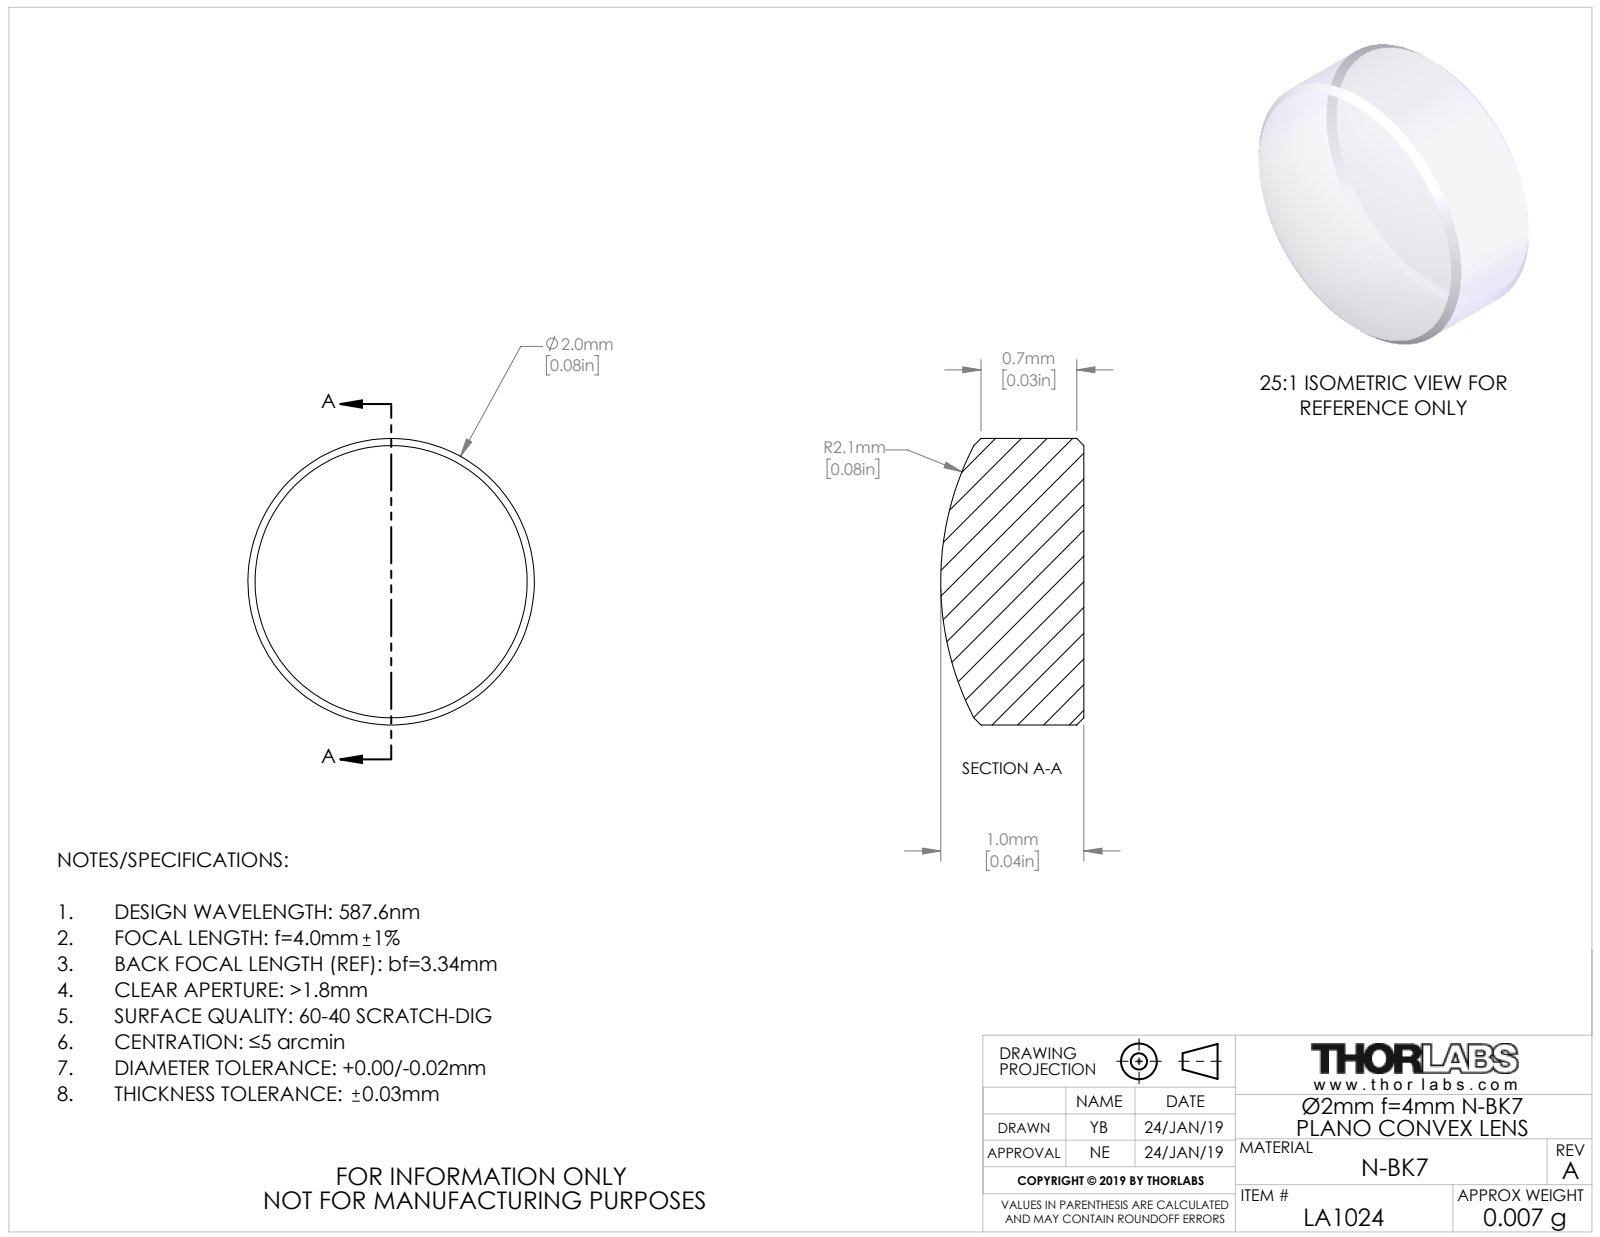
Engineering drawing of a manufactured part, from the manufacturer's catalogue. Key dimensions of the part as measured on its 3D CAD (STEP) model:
Part name (STEP PRODUCT): TTN162578-E0W
STEP written by: SolidWorks 2018 (CONFIG_CONTROL_DESIGN)
Units: millimetres
Bodies: 1 solid, 9 faces (1 planar, 2 cylindrical, 6 other)
Overall size (bounding box): 2 × 2 × 1
Volume: 3 mm³ · Surface area: 11 mm²
Round bosses / shafts (diameter × count): ⌀2 ×1
